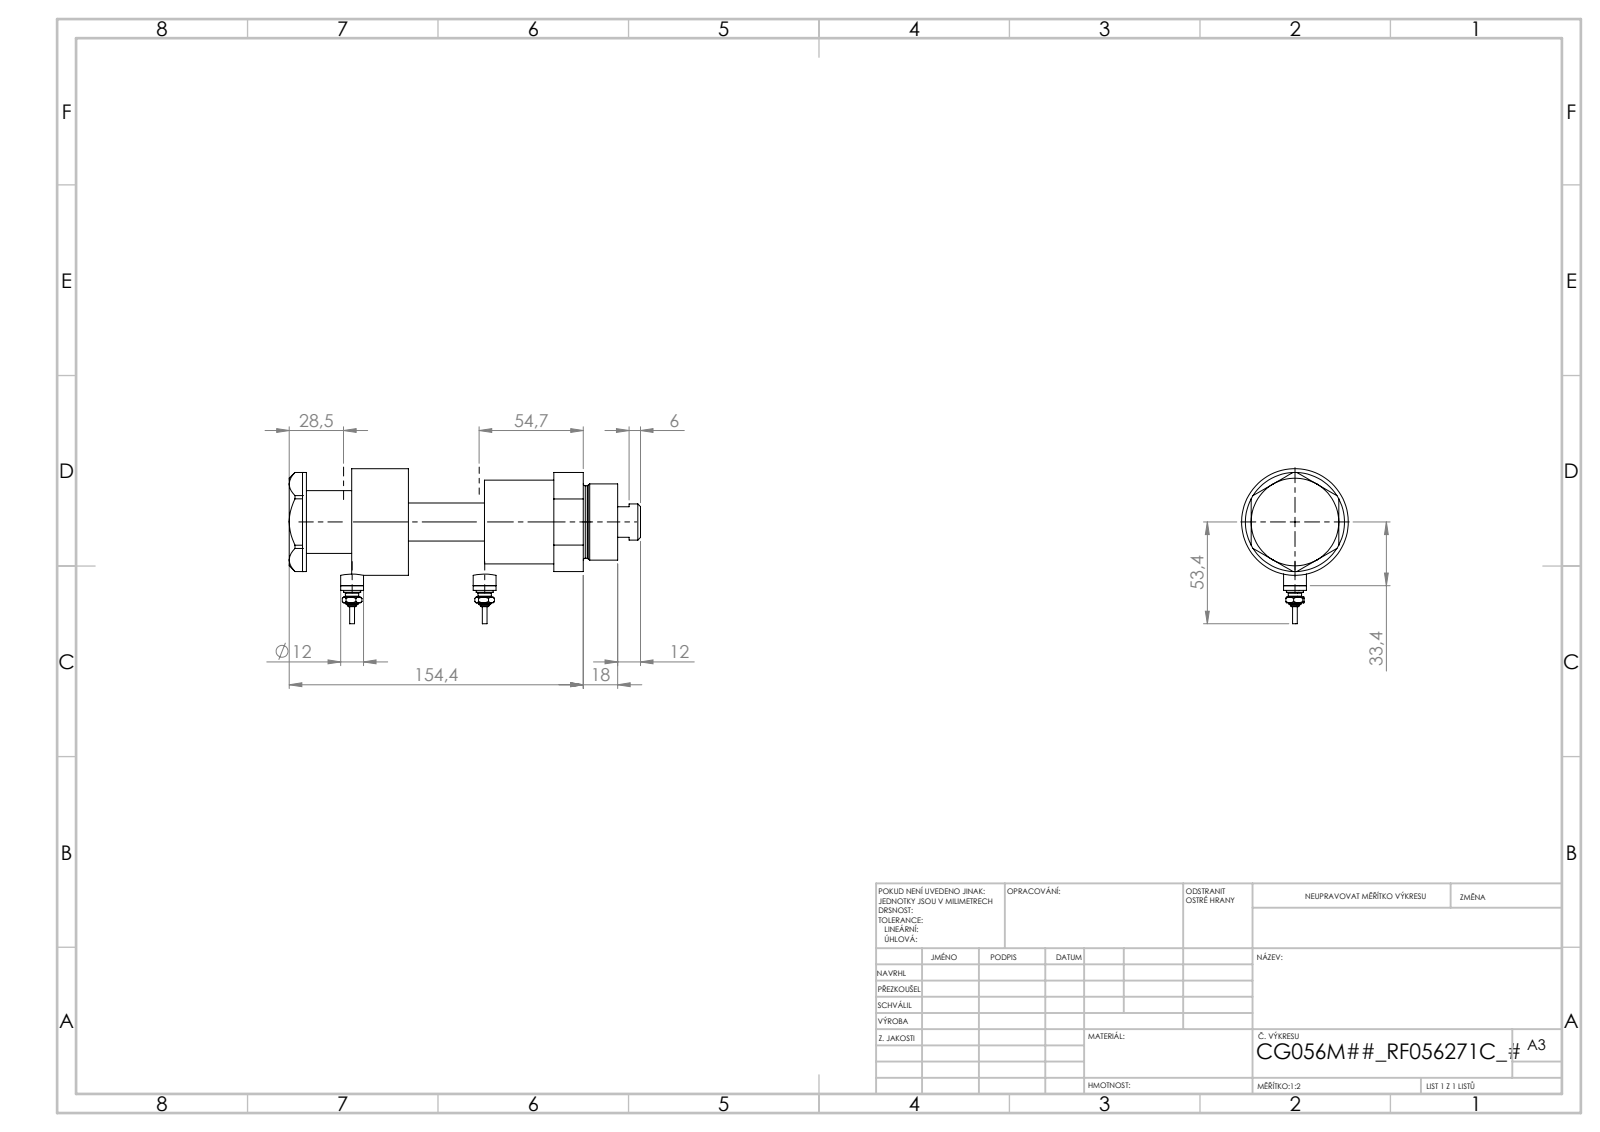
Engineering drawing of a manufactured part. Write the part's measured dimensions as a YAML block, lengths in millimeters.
part_name: "V270CG_SWITCH; V270CG_MIDDLE; V270CG_VC; V270CG_FRONT (+1 more)"
step_written_by: "SolidWorks 2019 (CONFIG_CONTROL_DESIGN)"
units: millimeters
bodies: {solids: 6, faces: 246, planar: 97, cylindrical: 75, other: 74}
overall_size: [184.4, 86.3, 56]
volume: 433072
surface_area: 80011
round_holes:
  - {diameter: 5, count: 2}
  - {diameter: 9.64, count: 2}
  - {diameter: 12.5, count: 2}
  - {diameter: 15, count: 2}
  - {diameter: 6.5, count: 1}
  - {diameter: 20, count: 1}
  - {diameter: 21.5, count: 1}
  - {diameter: 33, count: 1}
  - {diameter: 44, count: 1}
round_bosses_or_shafts:
  - {diameter: 12, count: 2}
  - {diameter: 9, count: 2}
  - {diameter: 7, count: 2}
  - {diameter: 4.34, count: 2}
  - {diameter: 2.4, count: 2}
  - {diameter: 56, count: 1}
  - {diameter: 52, count: 1}
  - {diameter: 40, count: 1}
face_to_face_distances: [23.8, 93.5, 69.7, 53.55, 29.75, 39.95, 9, 32.8, 62.55, 102.5]
hole_center_spacings: [2.9, 4.5, 66.7, 69.6, 71.2, 74.1]
